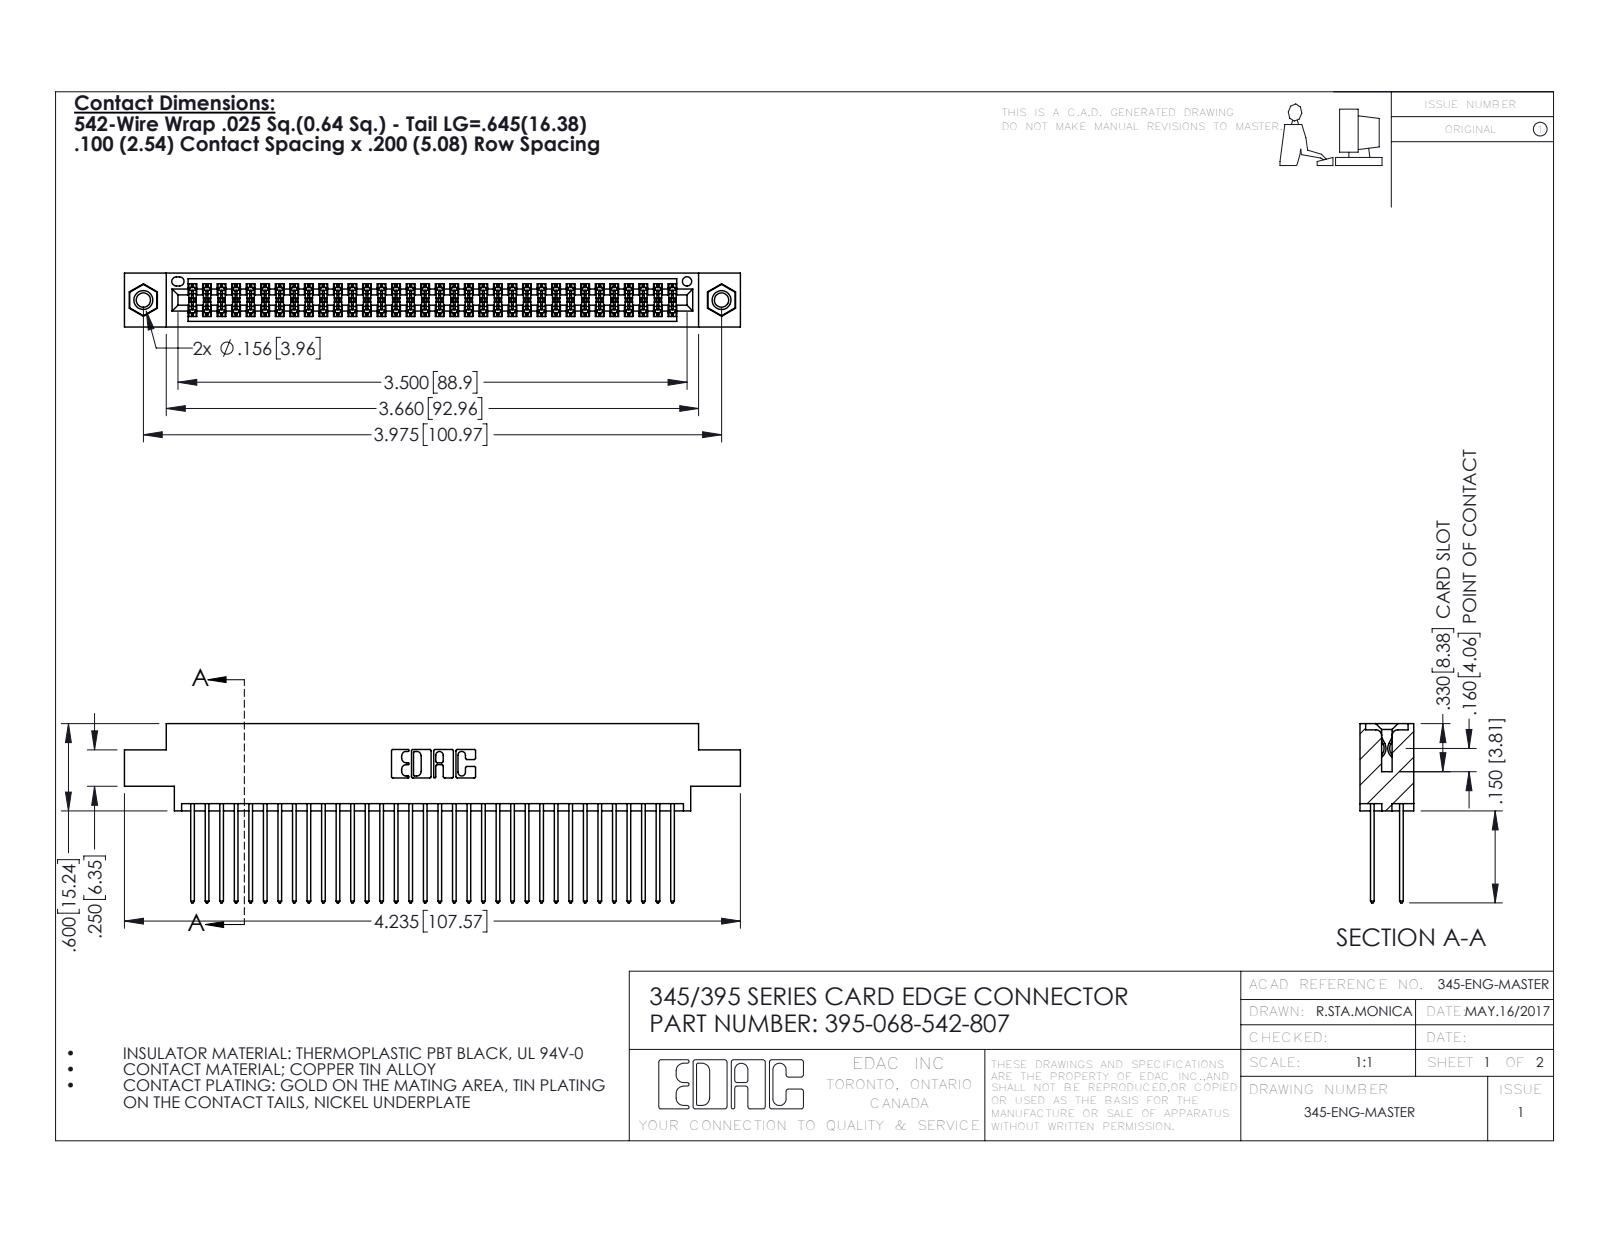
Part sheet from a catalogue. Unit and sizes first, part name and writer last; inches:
Units: inches
Overall size (bounding box): 4.235 × 1.232 × 0.37
Round holes (diameter × count): ⌀0.098 ×2, ⌀0.125 ×2, ⌀0.156 ×2, ⌀0.064 ×1
Round bosses / shafts (diameter × count): ⌀0.155 ×2
Partial cylindrical surfaces — rounded edges, fillets, slot ends (radius × count): R0.006 ×102, R0.01 ×68, R0.01 ×22, R0.007 ×6, R0.031 ×6, R0.026 ×3, R0.014 ×2, R0.019 ×2
Main face-to-face distances: 0.072, 0.298, 0.2, 0.098, 0.272, 0.025, 0.37, 0.225, 0.175, 0.149
Hole centre spacings: 0.27, 3.74, 3.975
Volume: 0.645 in³ · Surface area: 26.53 in²
Bodies: 71 solids, 3590 faces (2360 planar, 1214 cylindrical, 16 other)
Part name (STEP PRODUCT): 345-250-001_345-250-005-103; 345-292-001_345-293-142; 395-068-542-807; 345 Part_0.170 Offset - 0.156 Dia-TI
STEP written by: SolidWorks 2016 (CONFIG_CONTROL_DESIGN)
